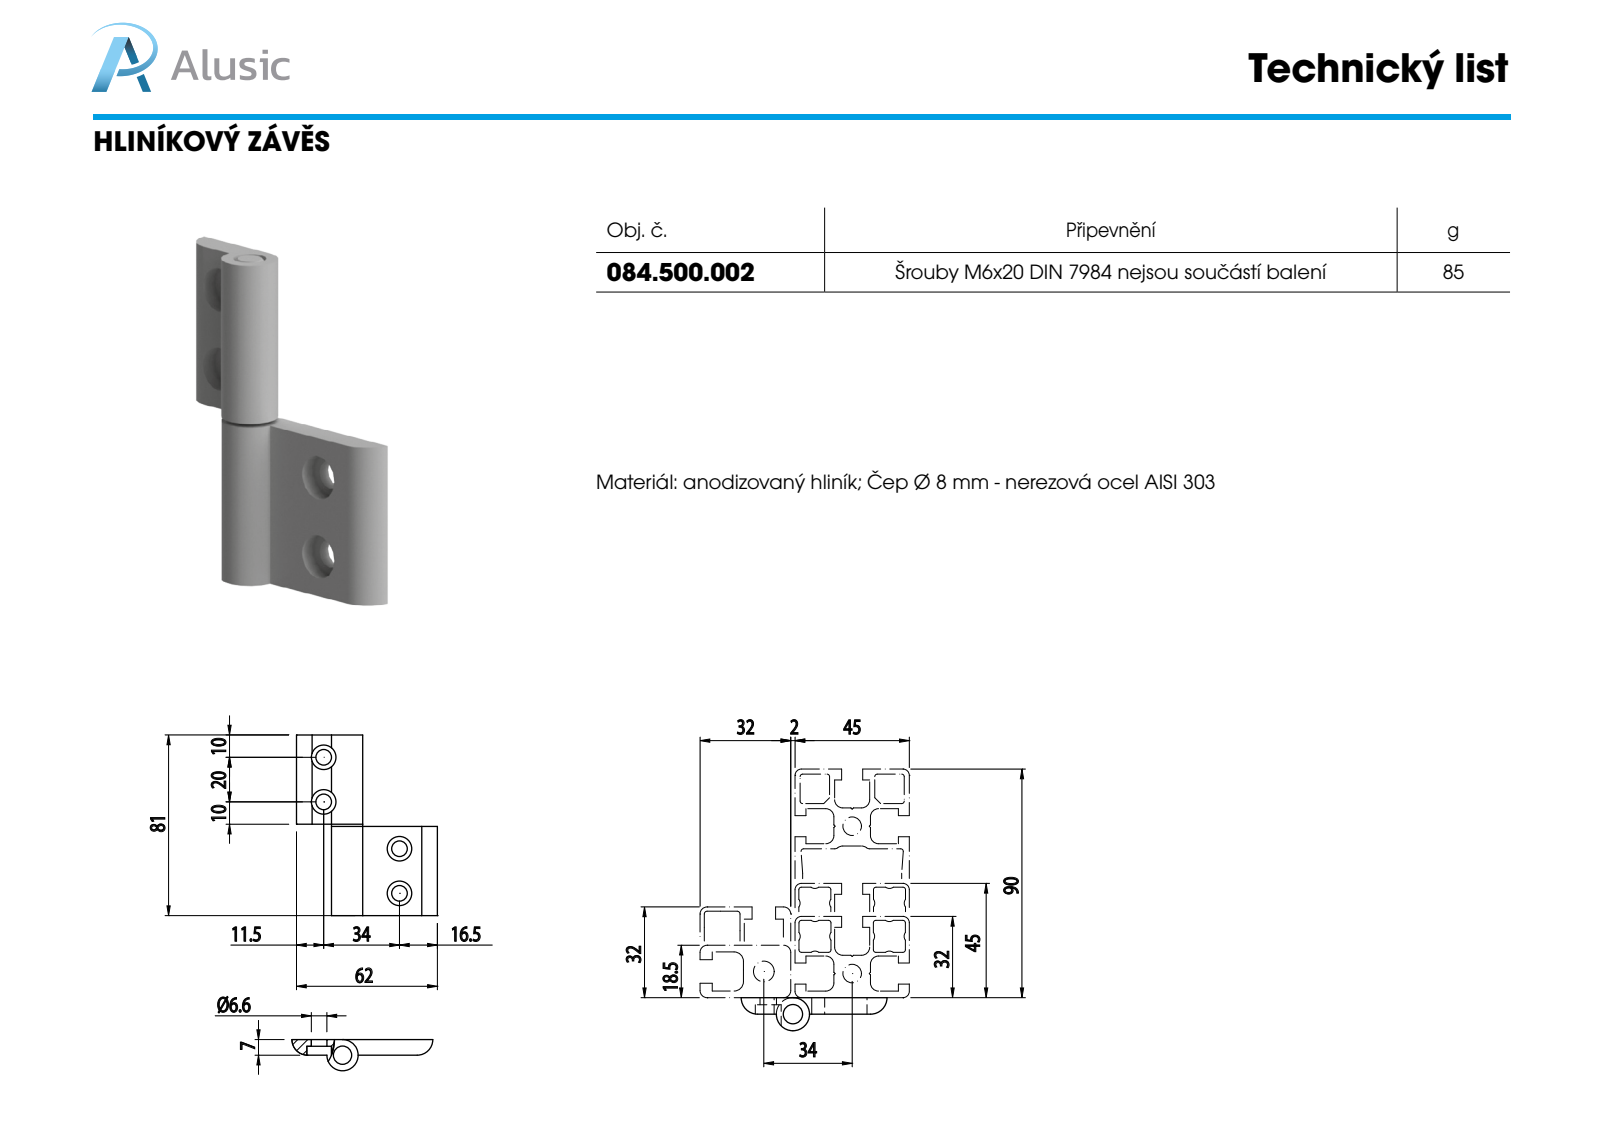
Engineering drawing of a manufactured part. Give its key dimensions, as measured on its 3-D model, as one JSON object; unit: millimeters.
{"part_name": "SEMI CERNIERA_084.500.002.A; SEMI CERNIERA_084.500.001.A; 084.500.002; PERNO CERNIERA_084.500.001.B", "step_written_by": "SolidWorks 2016 (CONFIG_CONTROL_DESIGN)", "units": "millimeters", "bodies": {"solids": 3, "faces": 168, "planar": 136, "cylindrical": 28, "other": 4}, "overall_size": [81, 63.2, 14], "volume_mm3": 23853, "surface_area_mm2": 13287, "round_holes": [[7, 4], [11, 4], [8.2, 1]], "round_bosses_or_shafts": [[14, 1], [8, 1]], "partial_cylinders_radius": [[7, 2]], "face_to_face_distances": [7, 40, 80, 3, 4, 6.11, 1, 41, 81, 6.12], "hole_center_spacings": [20, 52.5, 39.45, 68.96]}
